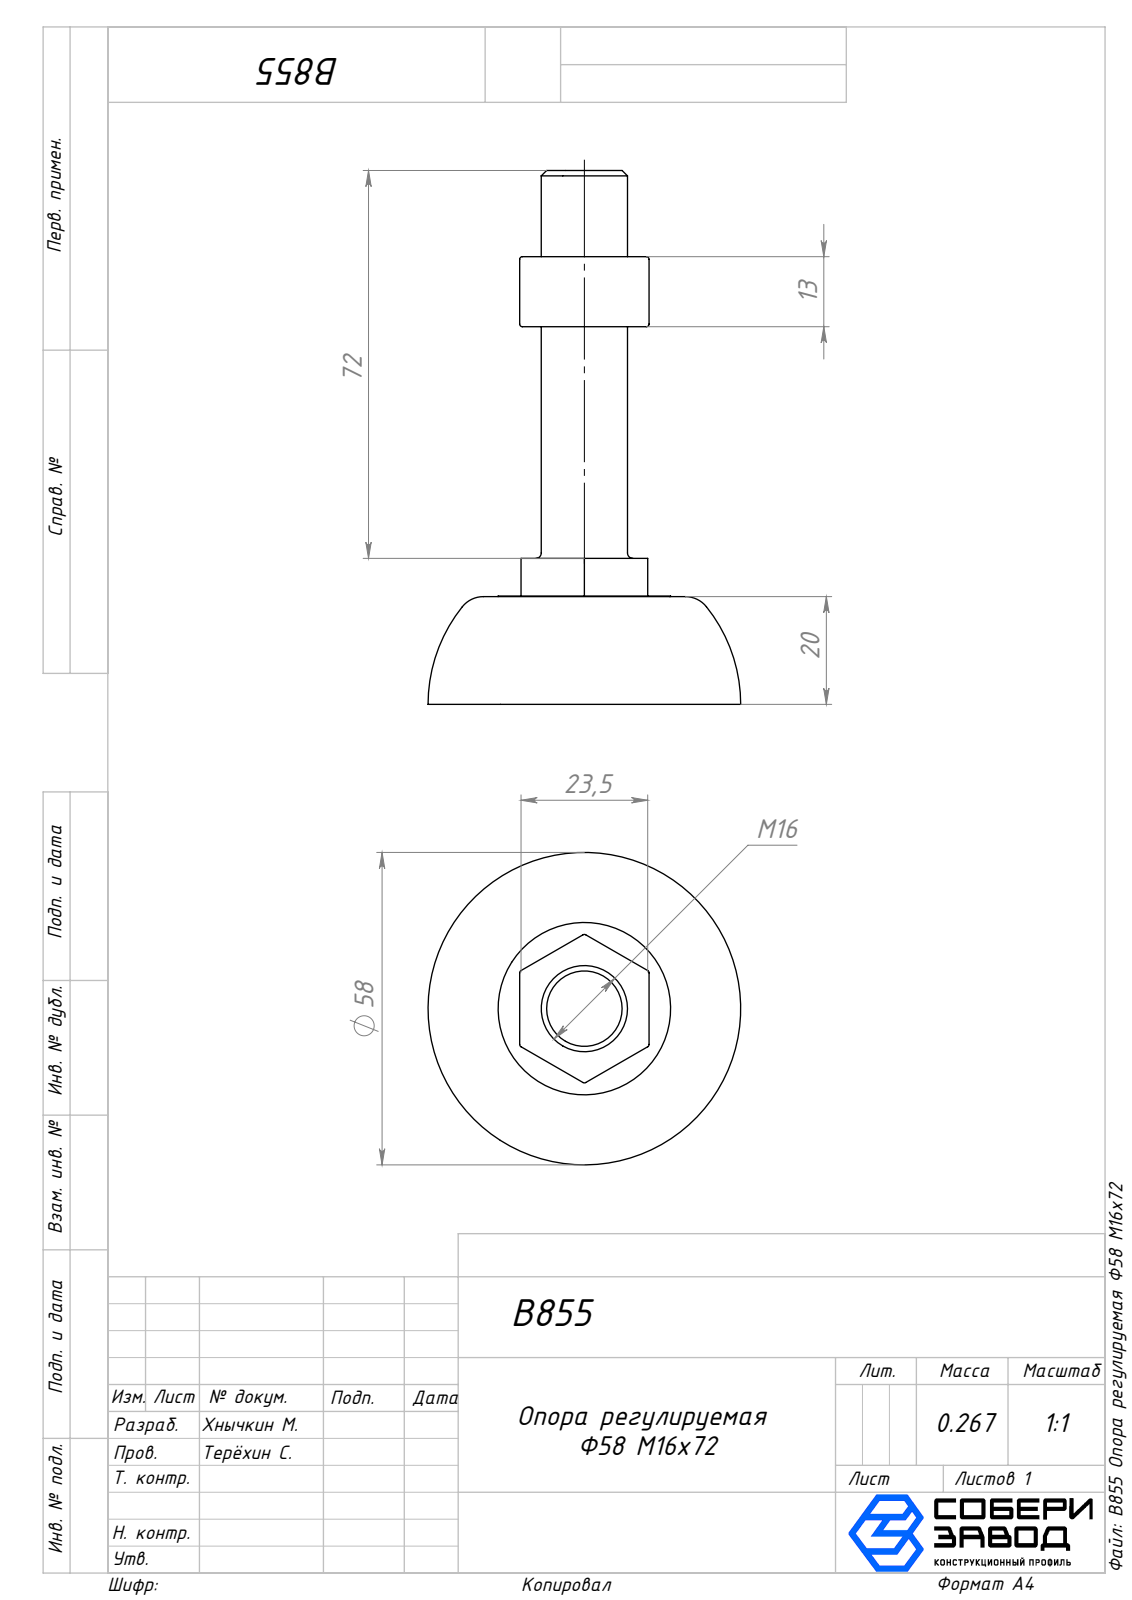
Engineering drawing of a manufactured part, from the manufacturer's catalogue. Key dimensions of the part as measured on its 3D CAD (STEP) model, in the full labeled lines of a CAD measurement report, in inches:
Part name (STEP PRODUCT): Мал. гайка_00; B855 Опора регулируемая Ф58 М16х72; Вал_00; Гайка_00 (+1 more)
STEP written by: SolidWorks 2025 (AUTOMOTIVE_DESIGN)
Units: inches
Bodies: 4 solids, 123 faces (30 planar, 48 cylindrical, 45 other)
Overall size (bounding box): 3.902 × 2.283 × 2.283
Volume: 2.22 in³ · Surface area: 26.85 in²
Round holes (diameter × count): ⌀0.157 ×1, ⌀0.197 ×1, ⌀0.551 ×1
Round bosses / shafts (diameter × count): ⌀1.26 ×1, ⌀0.63 ×1
Partial cylindrical surfaces — rounded edges, fillets, slot ends (radius × count): R0.02 ×36
Main face-to-face distances: 0.783, 0.791, 0.935, 0.945, 0.276, 0.787, 0.925, 3.272, 2.488, 2.484
